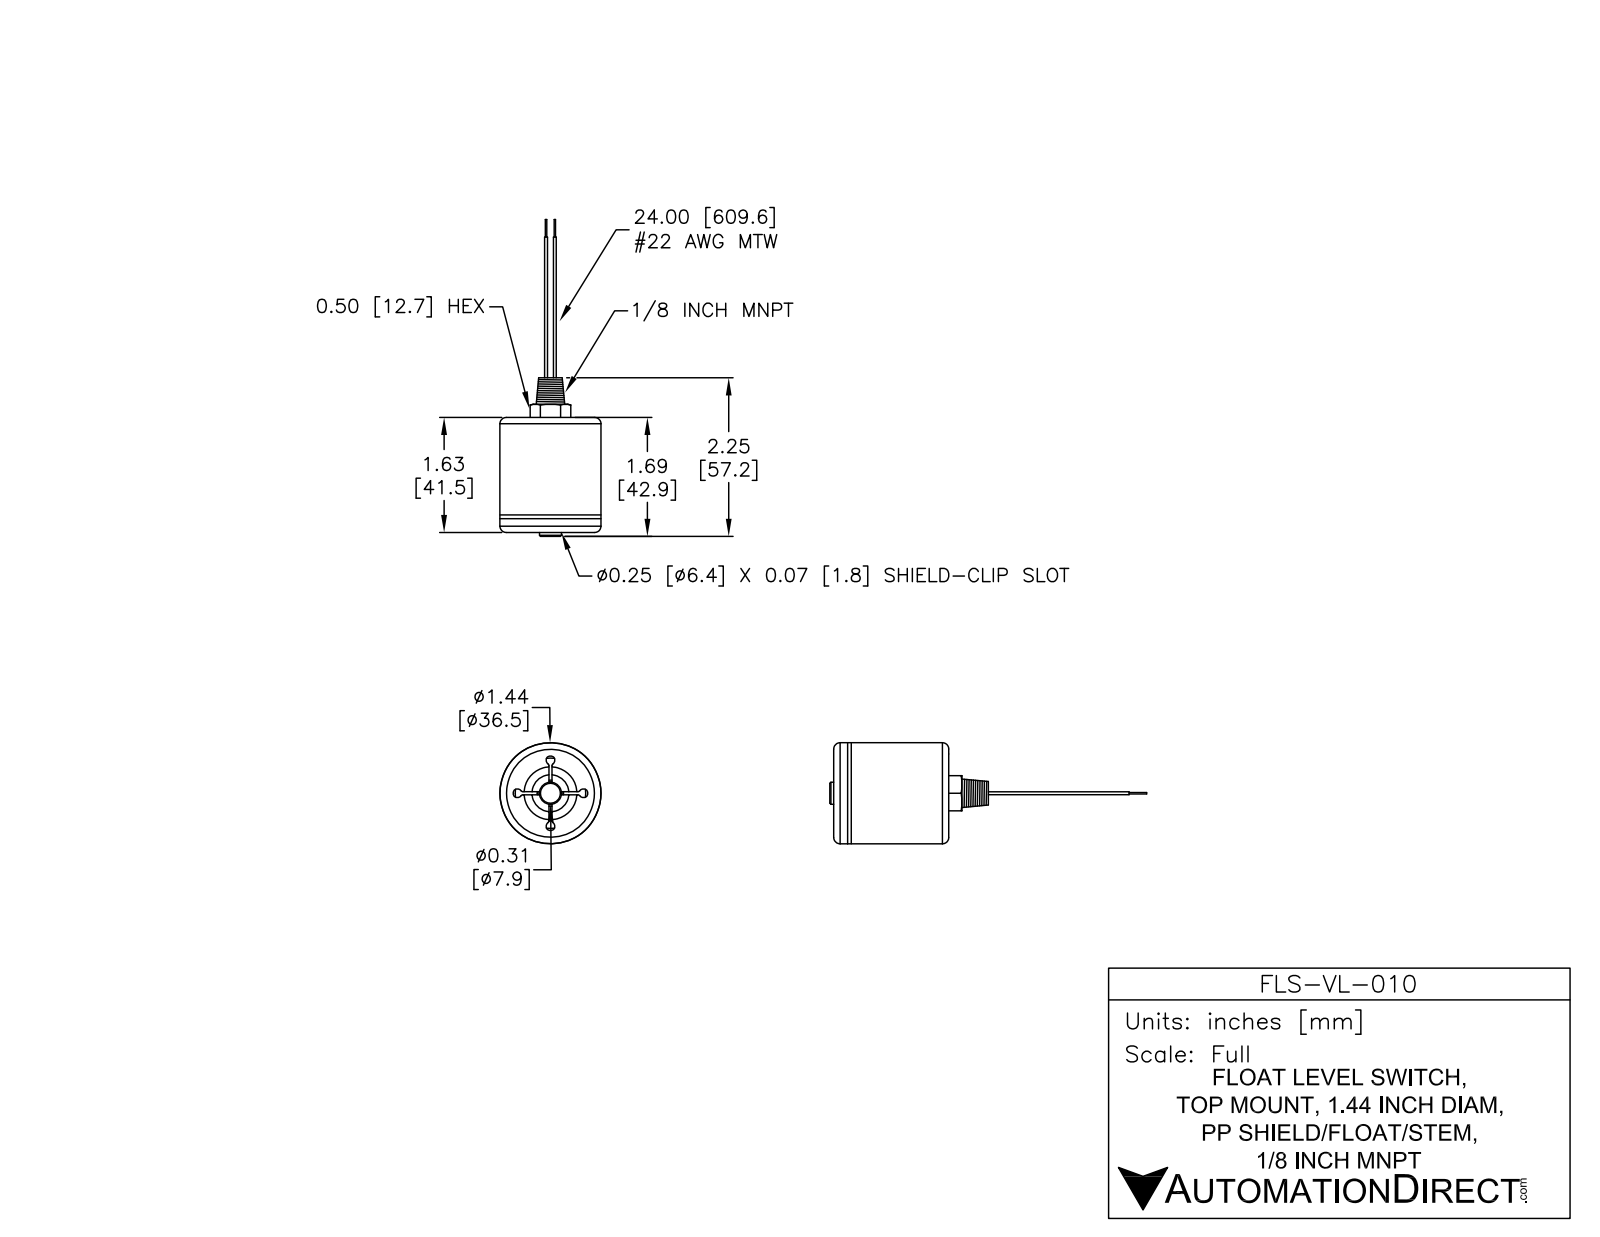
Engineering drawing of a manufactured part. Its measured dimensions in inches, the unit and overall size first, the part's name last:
Units: inches
Overall size (bounding box): 4.984 × 1.437 × 1.437
Round holes (diameter × count): ⌀0.125 ×4, ⌀1.312 ×1, ⌀1.393 ×1
Round bosses / shafts (diameter × count): ⌀0.04 ×4, ⌀0.02 ×2, ⌀1.437 ×1, ⌀0.873 ×1, ⌀0.313 ×1, ⌀0.313 ×1, ⌀0.25 ×1
Partial cylindrical surfaces — rounded edges, fillets, slot ends (radius × count): R0.164 ×2
Main face-to-face distances: 1.508, 1.477, 0.031, 0.11, 1.587, 1.618, 1.493, 1.383, 0.094, 0.125
Hole centre spacings: 0.5, 0.707, 1, 0.5, 0.5
Volume: 0.782 in³ · Surface area: 23.17 in²
Bodies: 2 solids, 125 faces (53 planar, 54 cylindrical, 18 other)
Part name (STEP PRODUCT): FLS-VL-010
STEP written by: SolidWorks 2013 (AUTOMOTIVE_DESIGN)
